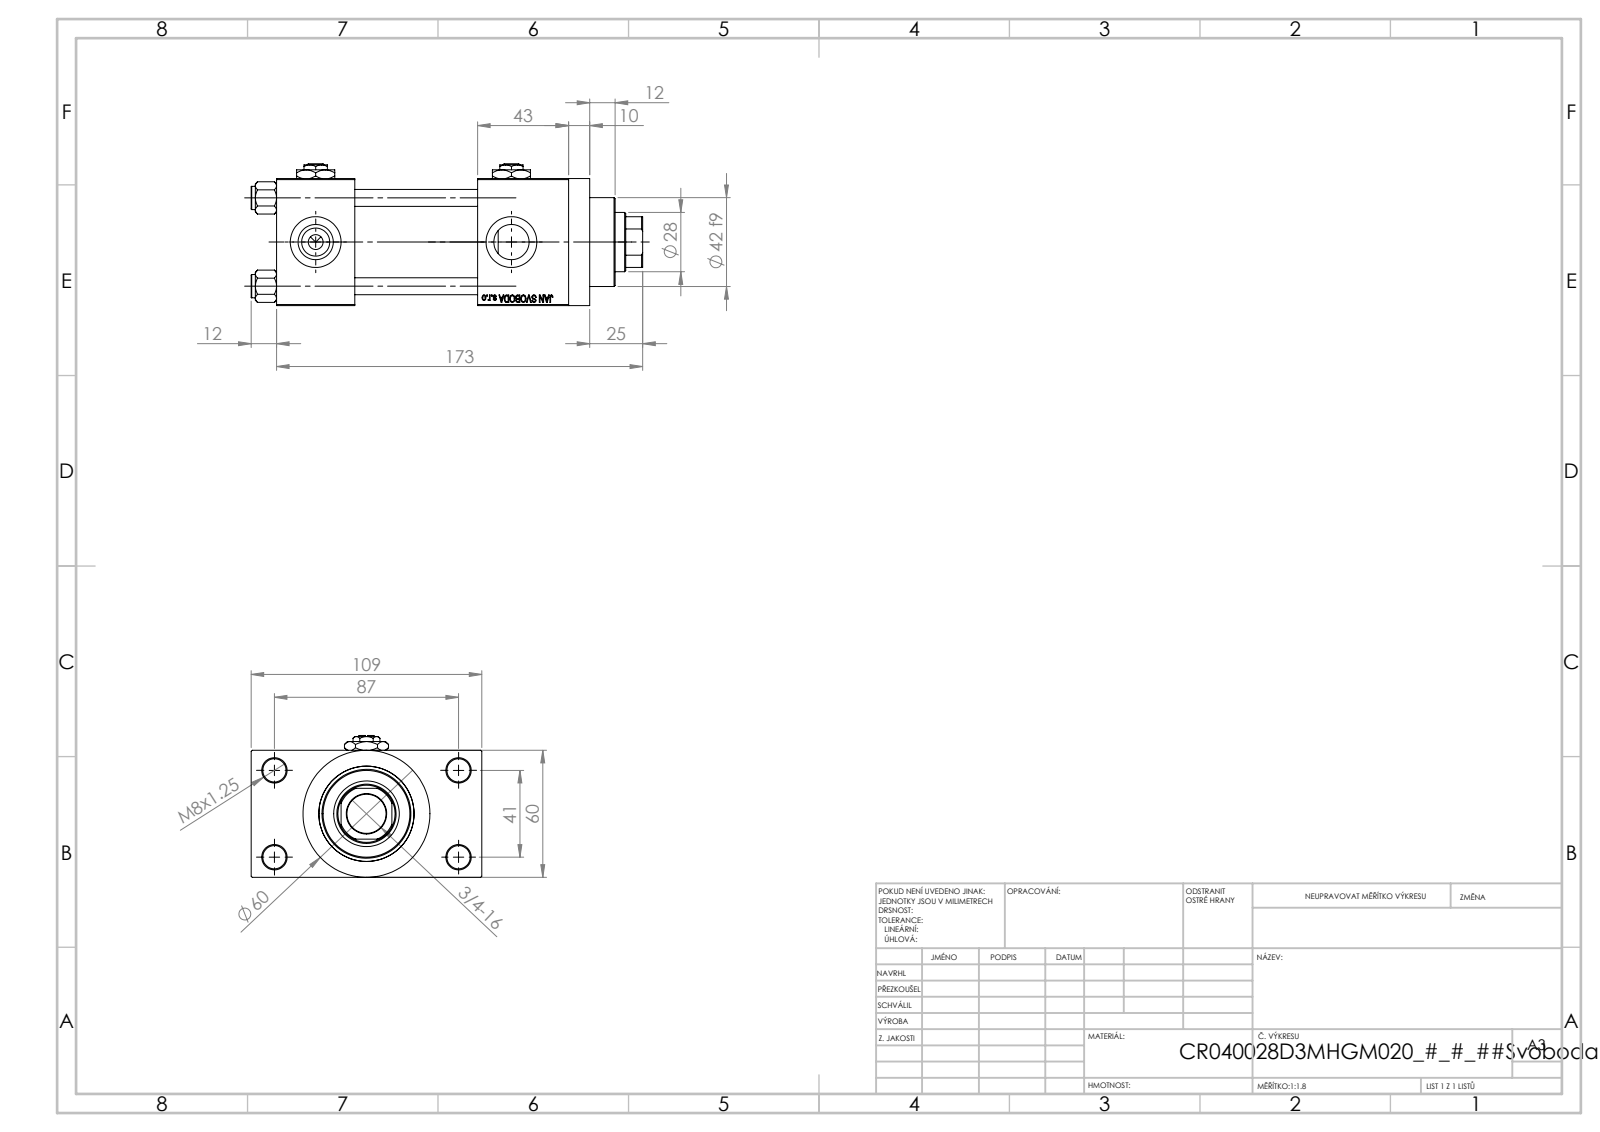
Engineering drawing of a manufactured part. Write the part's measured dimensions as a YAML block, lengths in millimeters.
part_name: "V215CR_D_TYCINKA; V215CR_D_Body; V215CR_VCP_D; V215_VC_A (+2 more)"
step_written_by: "SolidWorks 2019 (CONFIG_CONTROL_DESIGN)"
units: millimeters
bodies: {solids: 13, faces: 1205, planar: 546, cylindrical: 99, other: 560}
overall_size: [185, 109, 67]
volume: 526692
surface_area: 131752
round_holes:
  - {diameter: 8, count: 4}
  - {diameter: 11, count: 4}
  - {diameter: 16.66, count: 4}
  - {diameter: 24, count: 4}
  - {diameter: 7, count: 3}
  - {diameter: 18.5, count: 1}
  - {diameter: 28, count: 1}
  - {diameter: 31, count: 1}
  - {diameter: 40, count: 1}
  - {diameter: 45, count: 1}
round_bosses_or_shafts:
  - {diameter: 11, count: 4}
  - {diameter: 60, count: 1}
  - {diameter: 46, count: 1}
  - {diameter: 42, count: 1}
partial_cylinders:
  - {radius: 13.5, count: 1}
face_to_face_distances: [60, 58, 24.5, 84.5, 37, 95, 138, 101, 43, 109]
hole_center_spacings: [22.65, 29.49, 41.7, 47.15, 48.09, 64.35, 76.49, 41]
